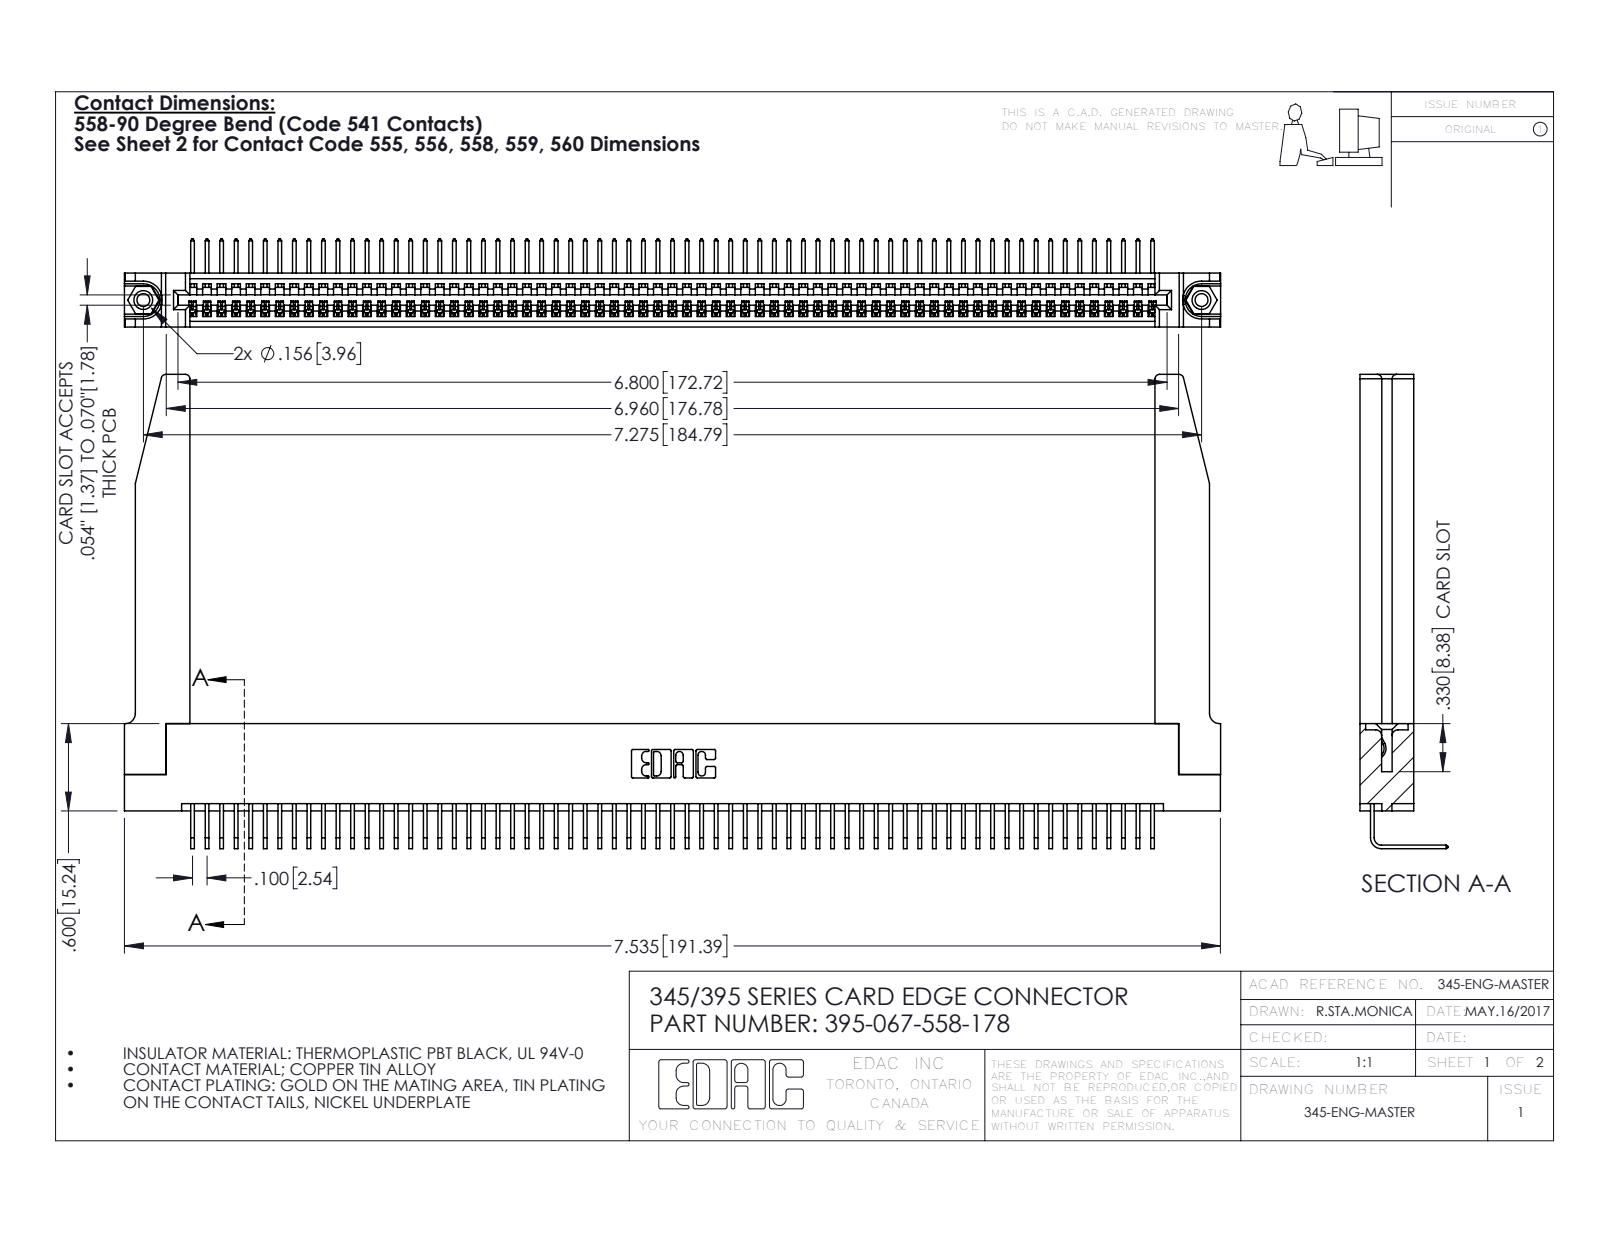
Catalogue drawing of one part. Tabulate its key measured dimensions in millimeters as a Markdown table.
| quantity | value |
| --- | --- |
| part name | 345-292-001_558 Tail - 2; 345 Part_Flush Mounting Lugs - 0.156 Dia-TH; 345-250-001_345-250-001-102; 345-220-078_345-220-078 (+1 more) |
| STEP written by | SolidWorks 2016 (CONFIG_CONTROL_DESIGN) |
| units | millimeters |
| bodies | 72 solids, 4380 faces (3036 planar, 1292 cylindrical, 52 other) |
| overall size | 191.4 × 82.8 × 15.4 |
| volume | 26 380 mm³ |
| surface area | 33 230 mm² |
| round holes (diameter × count) | 2.3 × 2, 3.2 × 2, 4 × 2, 1.6 × 1 |
| round bosses / shafts (diameter × count) | 3.9 × 2 |
| partial cylindrical surfaces (radius × count) | 0.2 × 134, 0.3 × 22, 0.8 × 8, 0.2 × 6, 0.8 × 6, 0.7 × 3, 0.8 × 2, 1 × 2 |
| main face-to-face distances | 1.8, 9.4, 7.6, 5.1, 2.5, 6.9, 0.6, 5.7, 3.8, 3.8 |
| hole center spacings | 6.9, 178.8, 184.8 |
